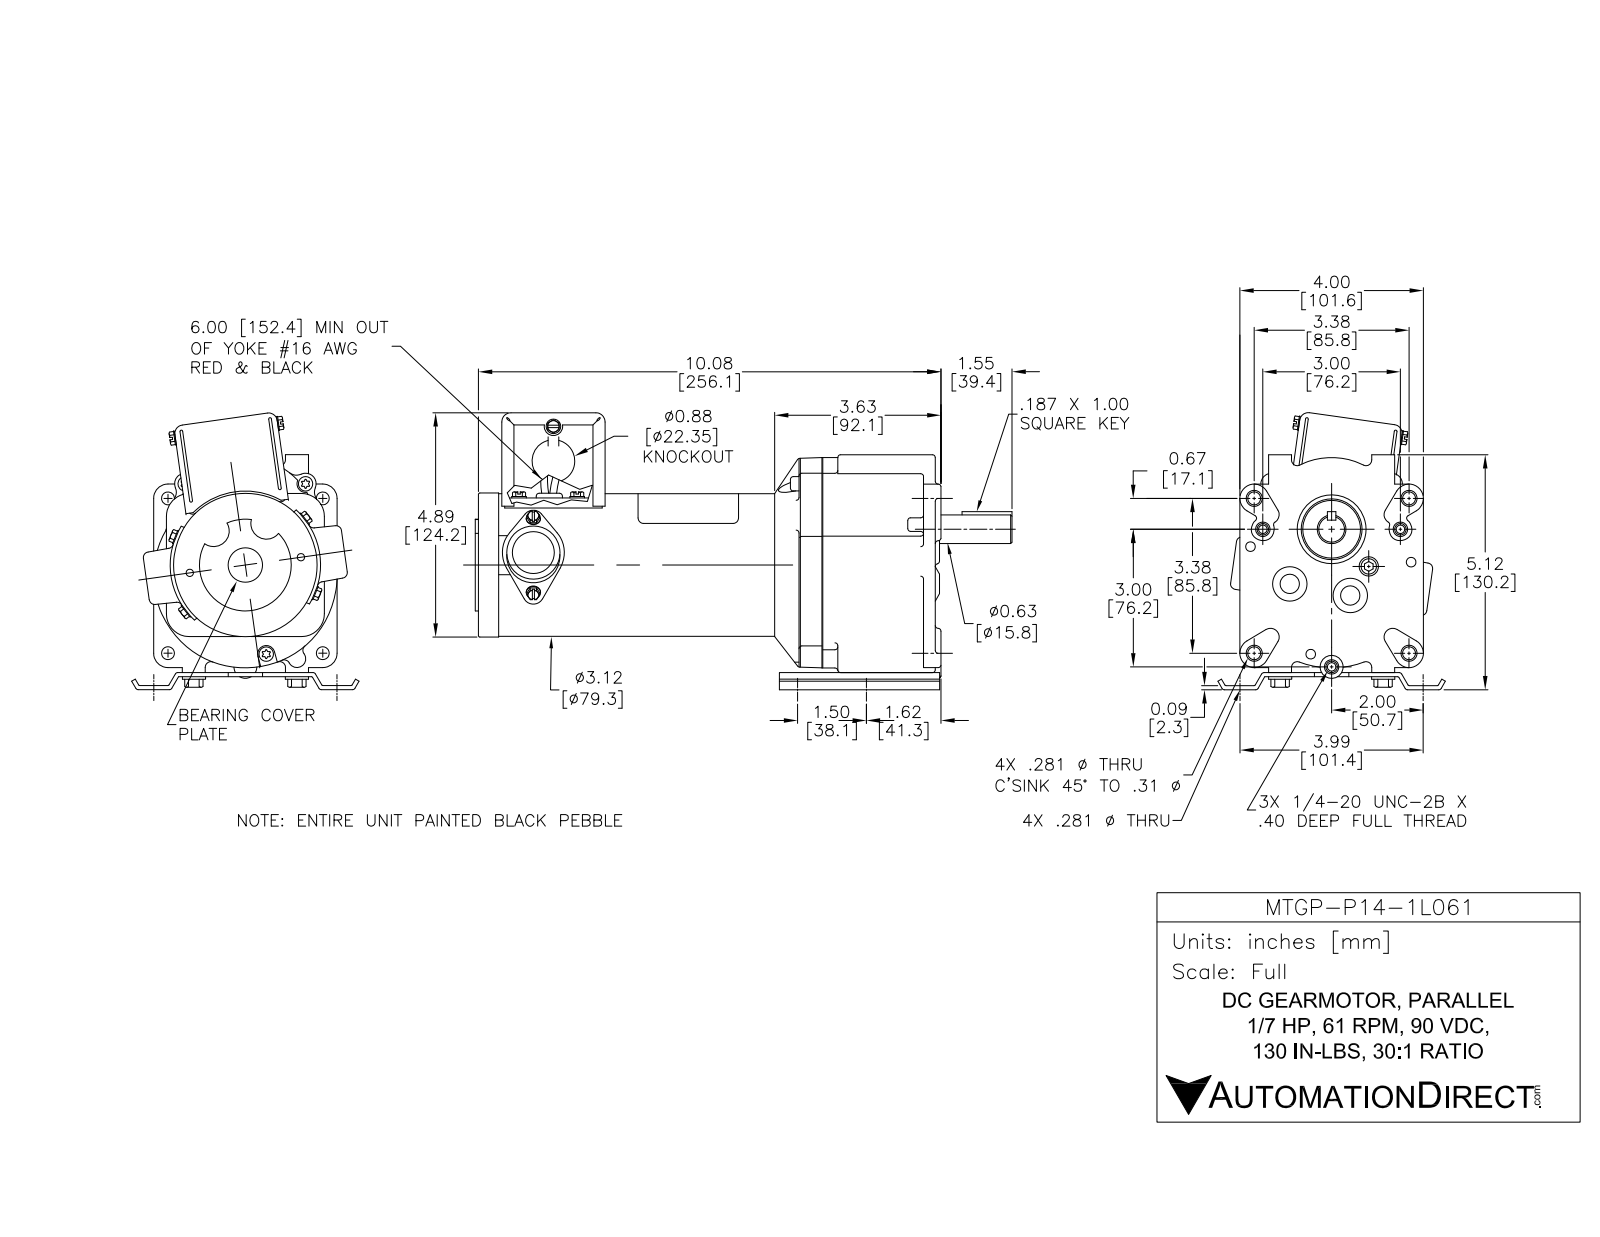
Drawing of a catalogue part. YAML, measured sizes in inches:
part_name: "MTGP-P14-1L061"
step_written_by: "SolidWorks 2014 (AUTOMOTIVE_DESIGN)"
units: inches
bodies: {solids: 53, faces: 984, planar: 567, cylindrical: 365, other: 52}
overall_size: [11.698, 6.209, 4.939]
volume: 65.11
surface_area: 470.6
round_holes:
  - {diameter: 0.3, count: 11}
  - {diameter: 0.5, count: 5}
  - {diameter: 0.25, count: 4}
  - {diameter: 0.345, count: 4}
  - {diameter: 0.21, count: 3}
  - {diameter: 0.125, count: 2}
  - {diameter: 0.198, count: 2}
  - {diameter: 0.208, count: 2}
  - {diameter: 0.345, count: 2}
  - {diameter: 0.375, count: 1}
  - {diameter: 0.46, count: 1}
  - {diameter: 0.625, count: 1}
round_bosses_or_shafts:
  - {diameter: 0.314, count: 5}
  - {diameter: 0.3, count: 4}
  - {diameter: 0.208, count: 3}
  - {diameter: 0.46, count: 2}
  - {diameter: 0.1, count: 2}
  - {diameter: 3.156, count: 1}
  - {diameter: 1.325, count: 1}
  - {diameter: 0.625, count: 1}
partial_cylinders:
  - {radius: 0.019, count: 28}
  - {radius: 0.1, count: 23}
  - {radius: 0.025, count: 8}
  - {radius: 0.25, count: 7}
  - {radius: 0.159, count: 4}
  - {radius: 0.19, count: 4}
  - {radius: 0.191, count: 4}
  - {radius: 0.234, count: 4}
face_to_face_distances: [1.375, 3.495, 2.12, 0.09, 0.031, 0.25, 0.063, 0.05, 1.425, 3.545]
hole_center_spacings: [1.62, 1.23, 1.5, 1.504, 1.603, 2.974, 3.375, 6.911]
